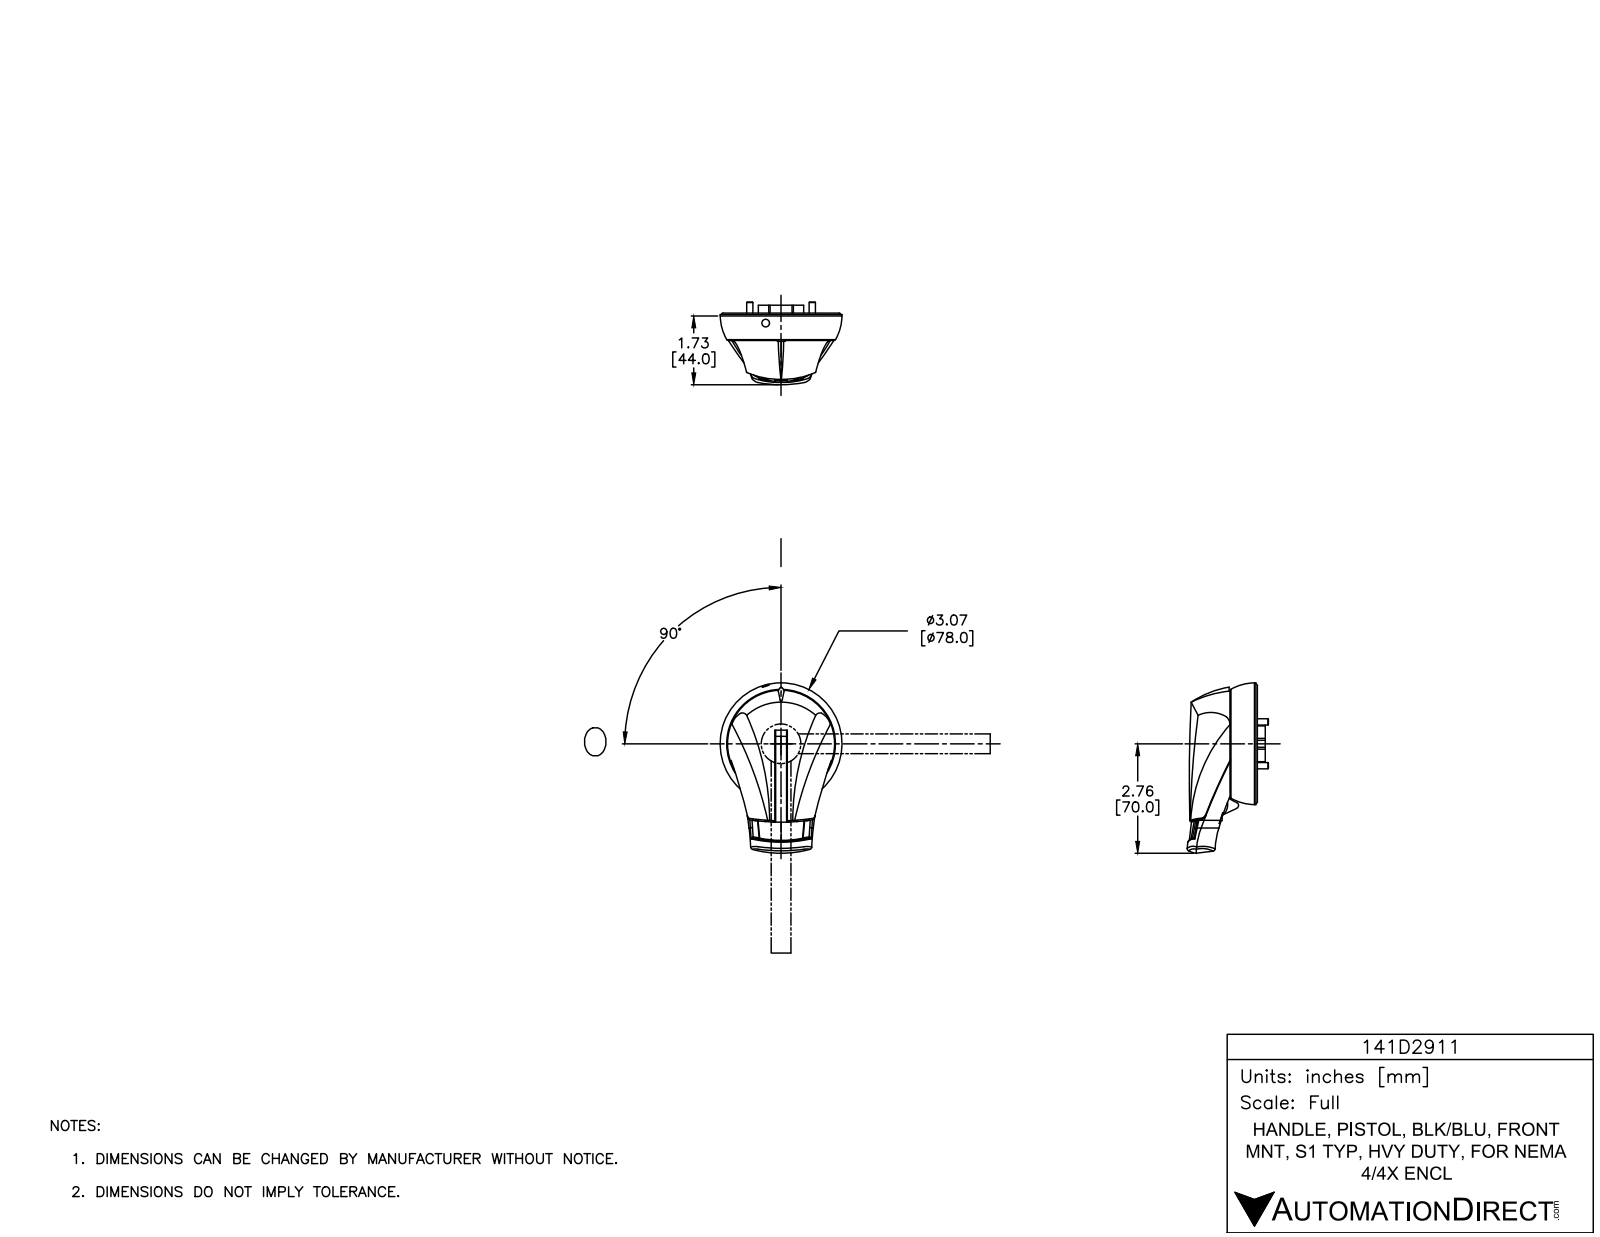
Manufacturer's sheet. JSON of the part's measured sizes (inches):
{"part_name": "141D2911", "step_written_by": "SolidWorks 2015 (AUTOMOTIVE_DESIGN)", "units": "inches", "bodies": {"solids": 8, "faces": 1516, "planar": 810, "cylindrical": 548, "other": 158}, "overall_size": [4.291, 3.07, 2.046], "volume_in3": 7.72, "surface_area_in2": 79.65, "round_holes": [[0.157, 6], [0.339, 4], [0.425, 4], [0.03, 3], [0.169, 2], [0.362, 2], [0.118, 1], [0.189, 1], [2.992, 1]], "round_bosses_or_shafts": [[0.02, 11], [0.335, 4], [0.315, 4], [0.089, 3], [0.069, 3], [0.228, 2], [2.819, 1], [2.701, 1]], "partial_cylinders_radius": [[0.01, 221], [0.015, 20], [0.034, 20], [0.03, 15], [0.039, 4], [0.025, 3], [5.437, 3], [0.079, 2]], "face_to_face_distances": [0.024, 0.701, 0.713, 0.689, 0.035, 0.102, 0.276, 0.173, 0.244, 0.047], "hole_center_spacings": [0.961, 0.309, 0.669, 1.098, 1.102, 1.203, 1.575, 1.881]}
